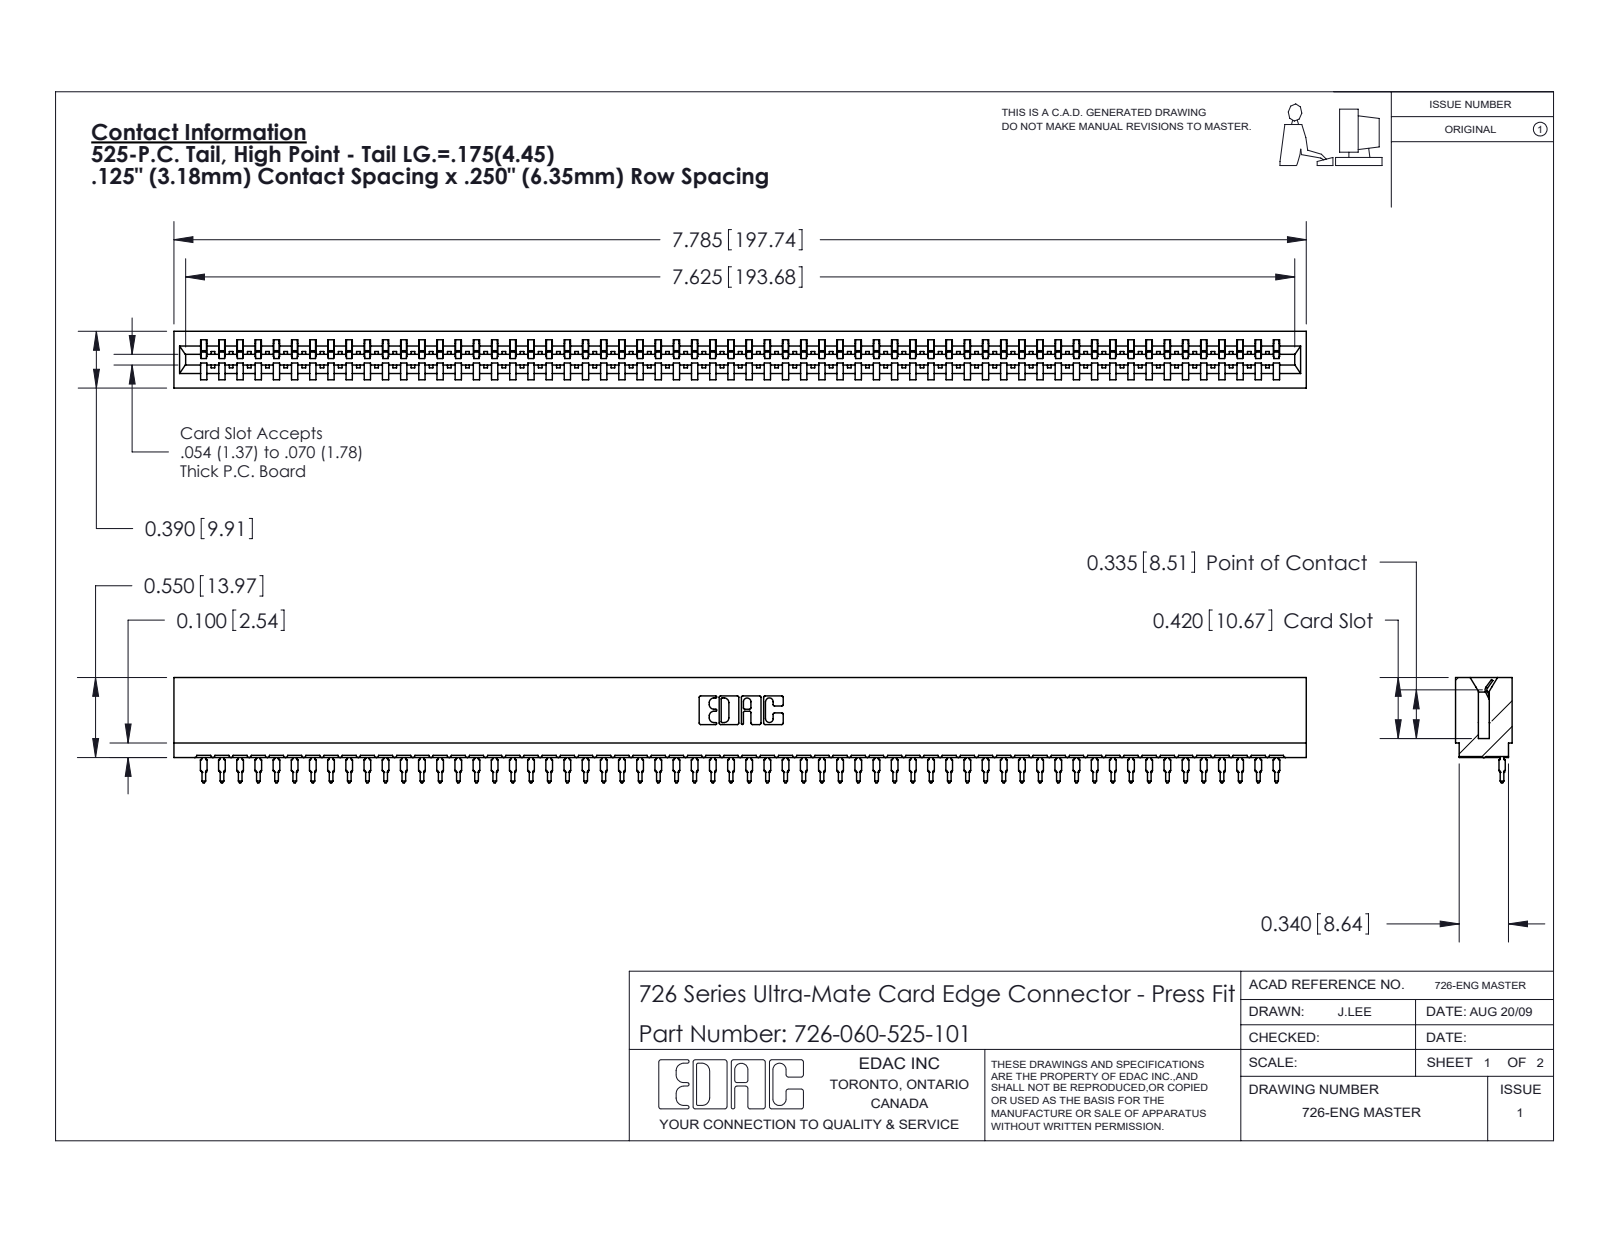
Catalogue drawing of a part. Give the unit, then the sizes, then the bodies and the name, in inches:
Units: inches
Overall size (bounding box): 7.785 × 0.724 × 0.39
Partial cylindrical surfaces — rounded edges, fillets, slot ends (radius × count): R0.021 ×120, R0.015 ×61, R0.01 ×22, R0.007 ×6, R0.031 ×6, R0.005 ×4, R0.011 ×4, R0.026 ×3
Main face-to-face distances: 0.057, 0.333, 0.39, 0.025, 0.307, 0.25, 0.275, 0.365, 0.032, 0.174
Volume: 1.067 in³ · Surface area: 41.32 in²
Bodies: 61 solids, 6577 faces (3835 planar, 1182 cylindrical, 1560 other)
Part name (STEP PRODUCT): 726-060-525-101; 746-292-001_525; 726 Part_.515 Slot Depth - 01
STEP written by: SolidWorks 2020 (CONFIG_CONTROL_DESIGN)
